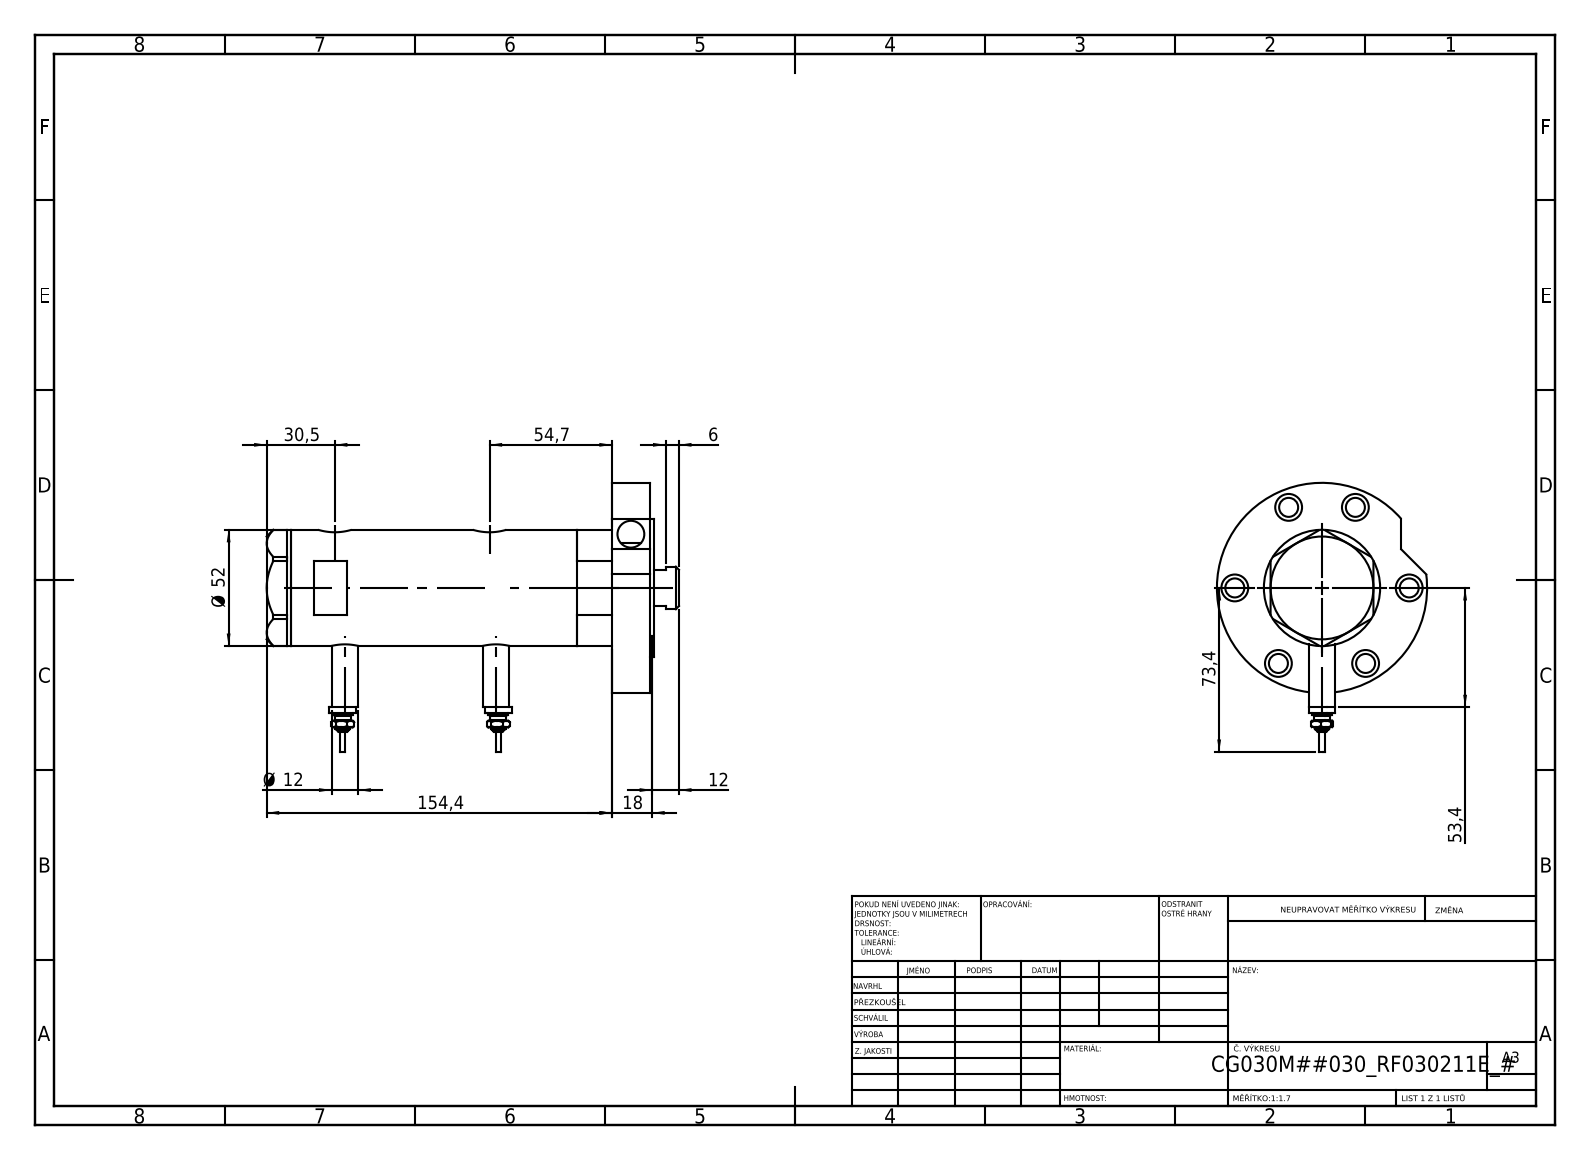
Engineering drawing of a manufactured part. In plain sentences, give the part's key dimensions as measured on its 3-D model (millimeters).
The part is named "V270CG_RF211E; V270CG_BACK; V270CG_VC; Switch (+2 more)". Its 3-D file was written by "SolidWorks 2019 (CONFIG_CONTROL_DESIGN)". It is 7 solids with 270 faces: 104 planar, 102 cylindrical and 64 other. Overall it measures 184.4 by 120.4 by 94 millimeters. Its volume is 422 746 cubic millimeters and its surface area 103 695 square millimeters. Round holes: 7 of diameter 12, 6 of diameter 8.5, 2 of diameter 9.73, 2 of diameter 12.5, 2 of diameter 15, 1 of diameter 6.5, 1 of diameter 20, 1 of diameter 21.5, 1 of diameter 30, 1 of diameter 33, 1 of diameter 40, 1 of diameter 44. Round bosses or shafts: 4 of diameter 12, 2 of diameter 9, 2 of diameter 7, 2 of diameter 4.5, 2 of diameter 2.5, 1 of diameter 94, 1 of diameter 62, 1 of diameter 52. The main face-to-face distances are 17, 143.4, 160.4, 2, 162.4, 91.5, 51.9, 68.9, 11, 173.4. The hole center spacings are 39, 43.34, 64.85, 67.55, 69.95, 77.83, 2.9, 4.5.
